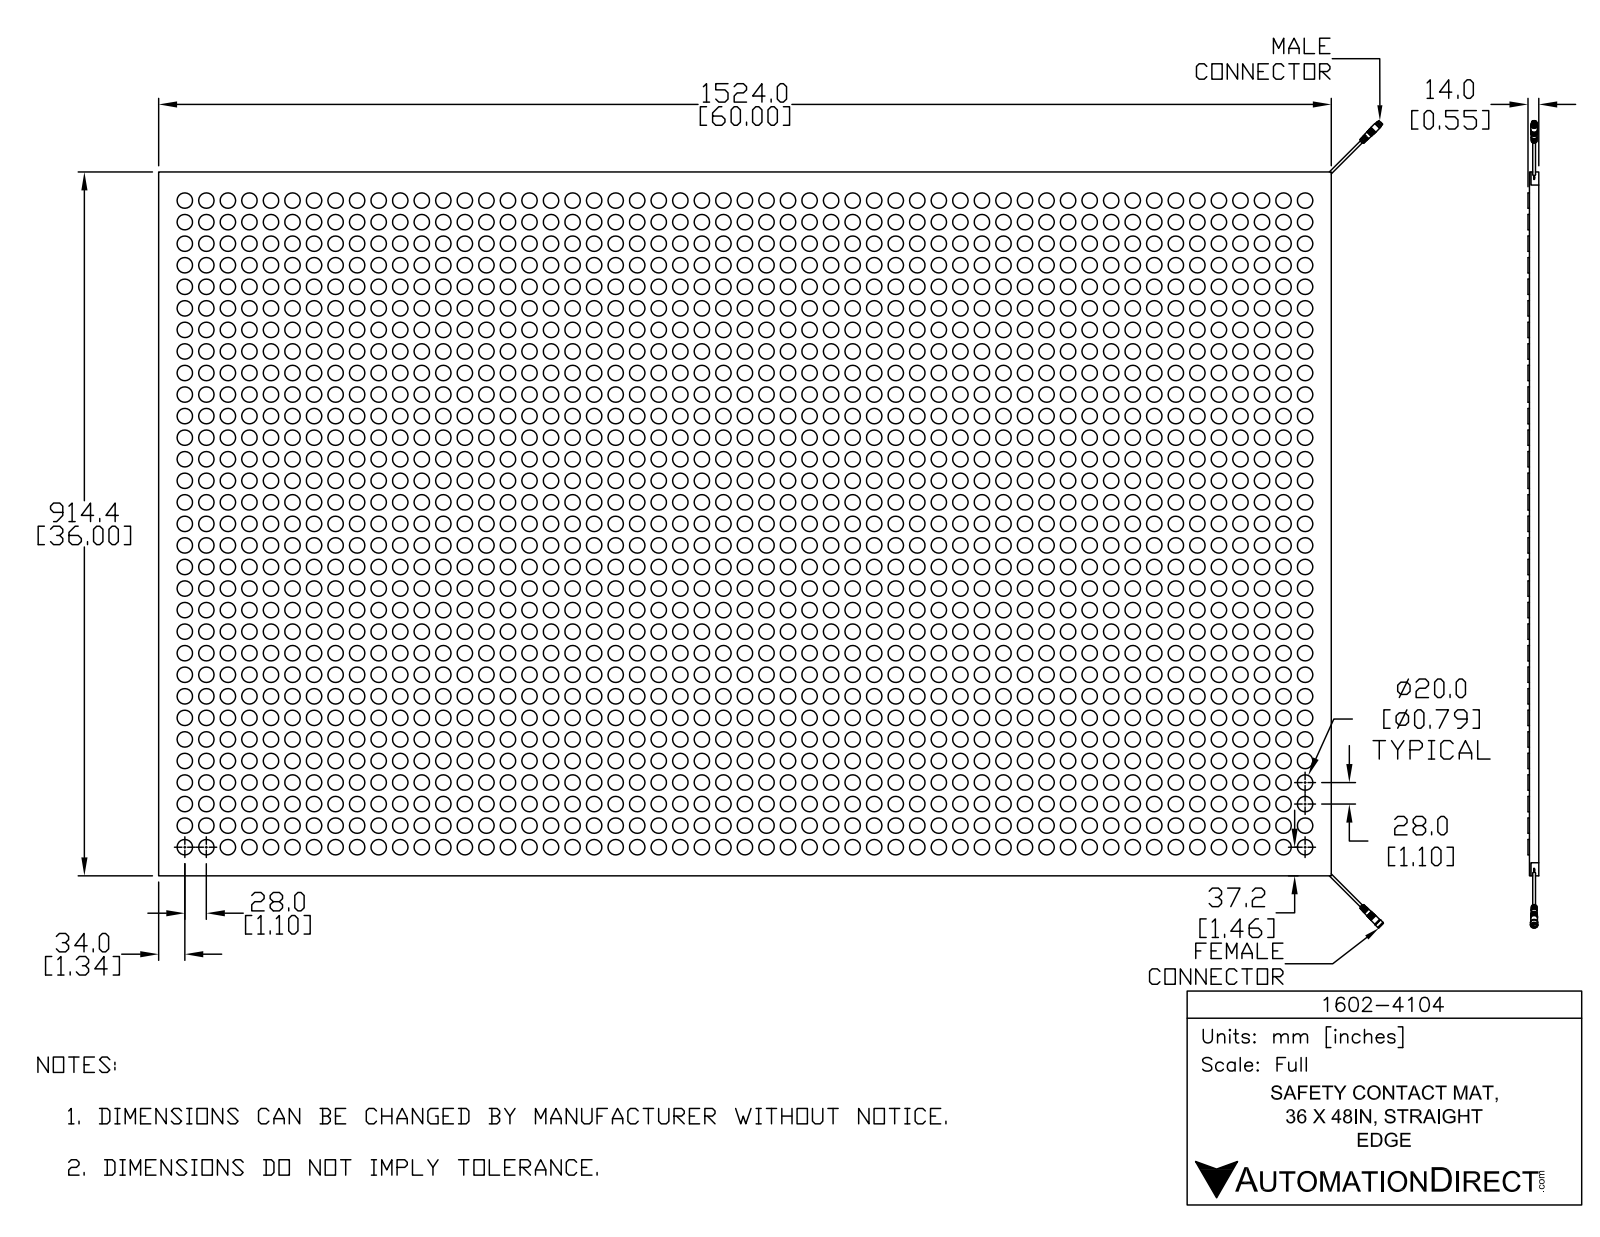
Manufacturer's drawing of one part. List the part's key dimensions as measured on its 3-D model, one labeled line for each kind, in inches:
Part name (STEP PRODUCT): 1602-4105_a
STEP written by: SolidWorks 2018 (AUTOMOTIVE_DESIGN)
Units: inches
Bodies: 6 solids, 3549 faces (1765 planar, 1702 cylindrical, 82 other)
Overall size (bounding box): 62.67 × 41.295 × 0.551
Volume: 1 084 in³ · Surface area: 4 738 in²
Round holes (diameter × count): ⌀0.063 ×3, ⌀0.134 ×2, ⌀0.228 ×1, ⌀0.232 ×1, ⌀0.272 ×1, ⌀0.283 ×1
Round bosses / shafts (diameter × count): ⌀0.787 ×1643, ⌀0.047 ×24, ⌀0.031 ×8, ⌀0.039 ×3, ⌀0.346 ×2, ⌀0.138 ×2, ⌀0.378 ×1, ⌀0.354 ×1
Main face-to-face distances: 0.472, 0.079, 0.551, 36, 60, 0.157, 0.394, 0.087, 0.039, 0.047
Hole centre spacings: 0.069, 0.098, 0.138
